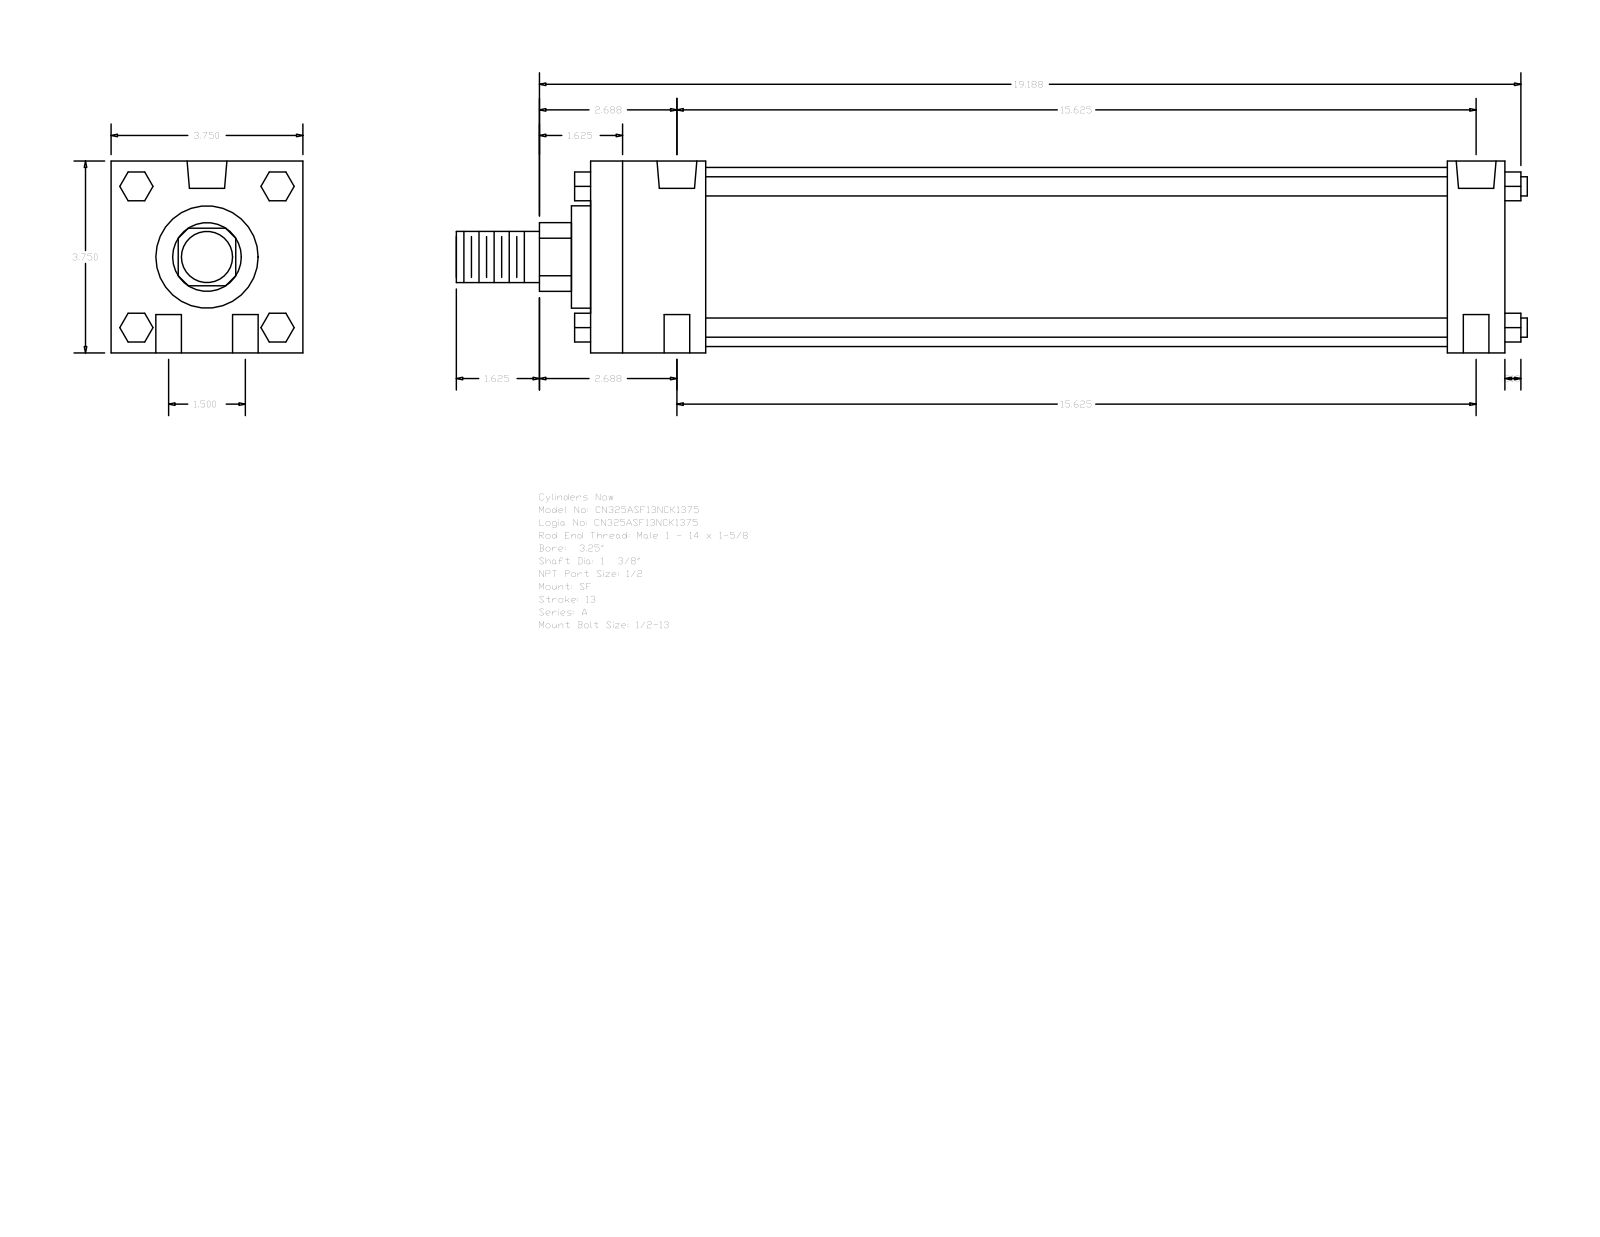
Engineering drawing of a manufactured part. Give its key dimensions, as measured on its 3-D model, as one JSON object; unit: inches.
{"part_name": "A_SF__0325_1.375", "step_written_by": "GSSL Pune (CONFIG_CONTROL_DESIGN)", "units": "inches", "bodies": {"solids": 0, "faces": 124, "planar": 94, "cylindrical": 30, "other": 0}, "overall_size": [20.937, 3.75, 3.75], "round_holes": [[0.5, 4], [0.344, 2], [0.778, 2]], "round_bosses_or_shafts": [[0.375, 4], [3.5, 1], [2, 1], [1.375, 1], [1, 1]], "partial_cylinders_radius": [[0.672, 1]], "face_to_face_distances": [3.75, 17.875, 2.25, 1.125, 16.75, 14.5, 15.625, 2.625, 0.375, 17.125], "hole_center_spacings": [0.75, 15.643, 15.625, 1.5, 15.697, 15.375]}
